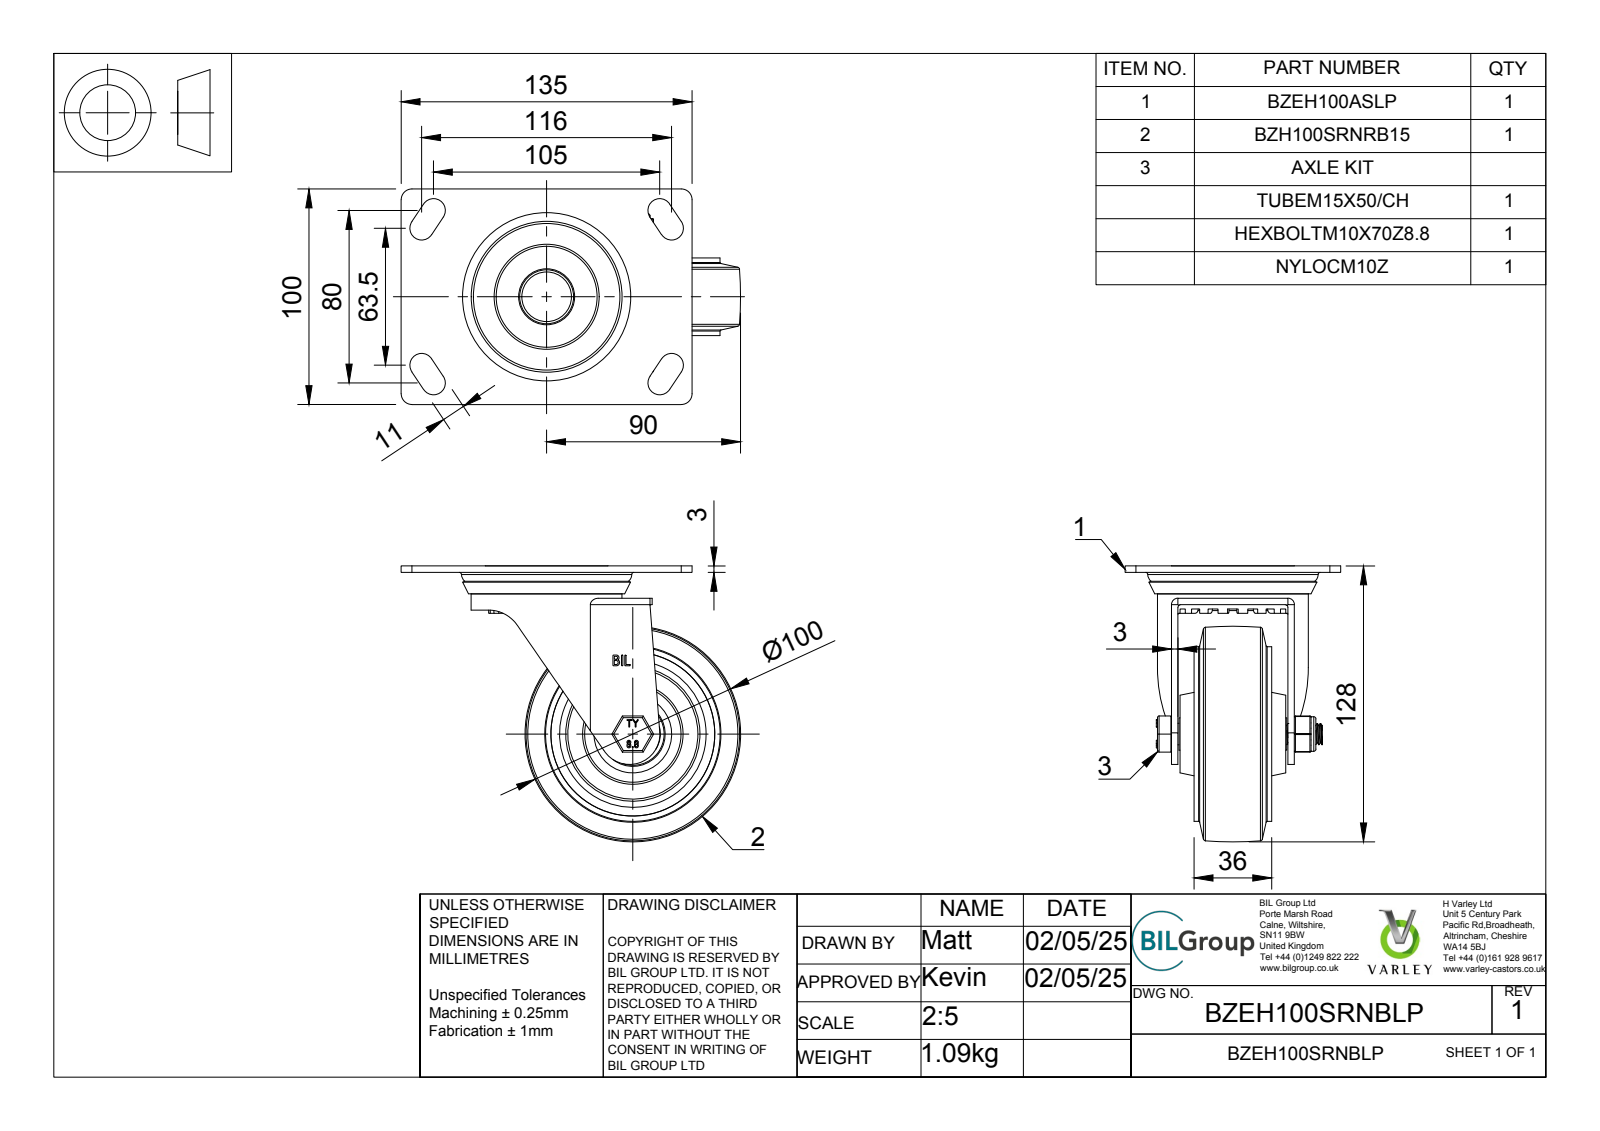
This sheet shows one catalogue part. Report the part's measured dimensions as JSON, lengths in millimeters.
{"part_name": "BZEH100SRNBLP v3; BZEH100ASLP v1; ZINC PLATED, PRESSED STEEL TOP PLATE; ZINC PLATED, PRESSED STEEL TOP PLATE Geometry (+7 more)", "step_written_by": "Autodesk Translation Framework v14.4.0.0 (AUTOMOTIVE_DESIGN)", "units": "millimeters", "bodies": {"solids": 38, "faces": 584, "planar": 305, "cylindrical": 137, "other": 142}, "overall_size": [157.5, 128, 100], "volume_mm3": 317459, "surface_area_mm2": 141186, "round_holes": [[30, 2], [10, 1], [10.2, 1], [10.5, 1], [12, 1], [15, 1], [23, 1], [64, 1], [76, 1]], "round_bosses_or_shafts": [[4, 8], [81, 1], [70, 1], [54, 1], [25, 1], [22.75, 1], [21, 1], [16, 1]], "partial_cylinders_radius": [[0.5, 18], [5.5, 8], [0.75, 6], [5, 4], [1.25, 3], [3, 2], [9.38, 1], [14.1, 1]], "face_to_face_distances": [3, 5, 10, 2, 7, 15, 54, 8, 4, 10.5]}
